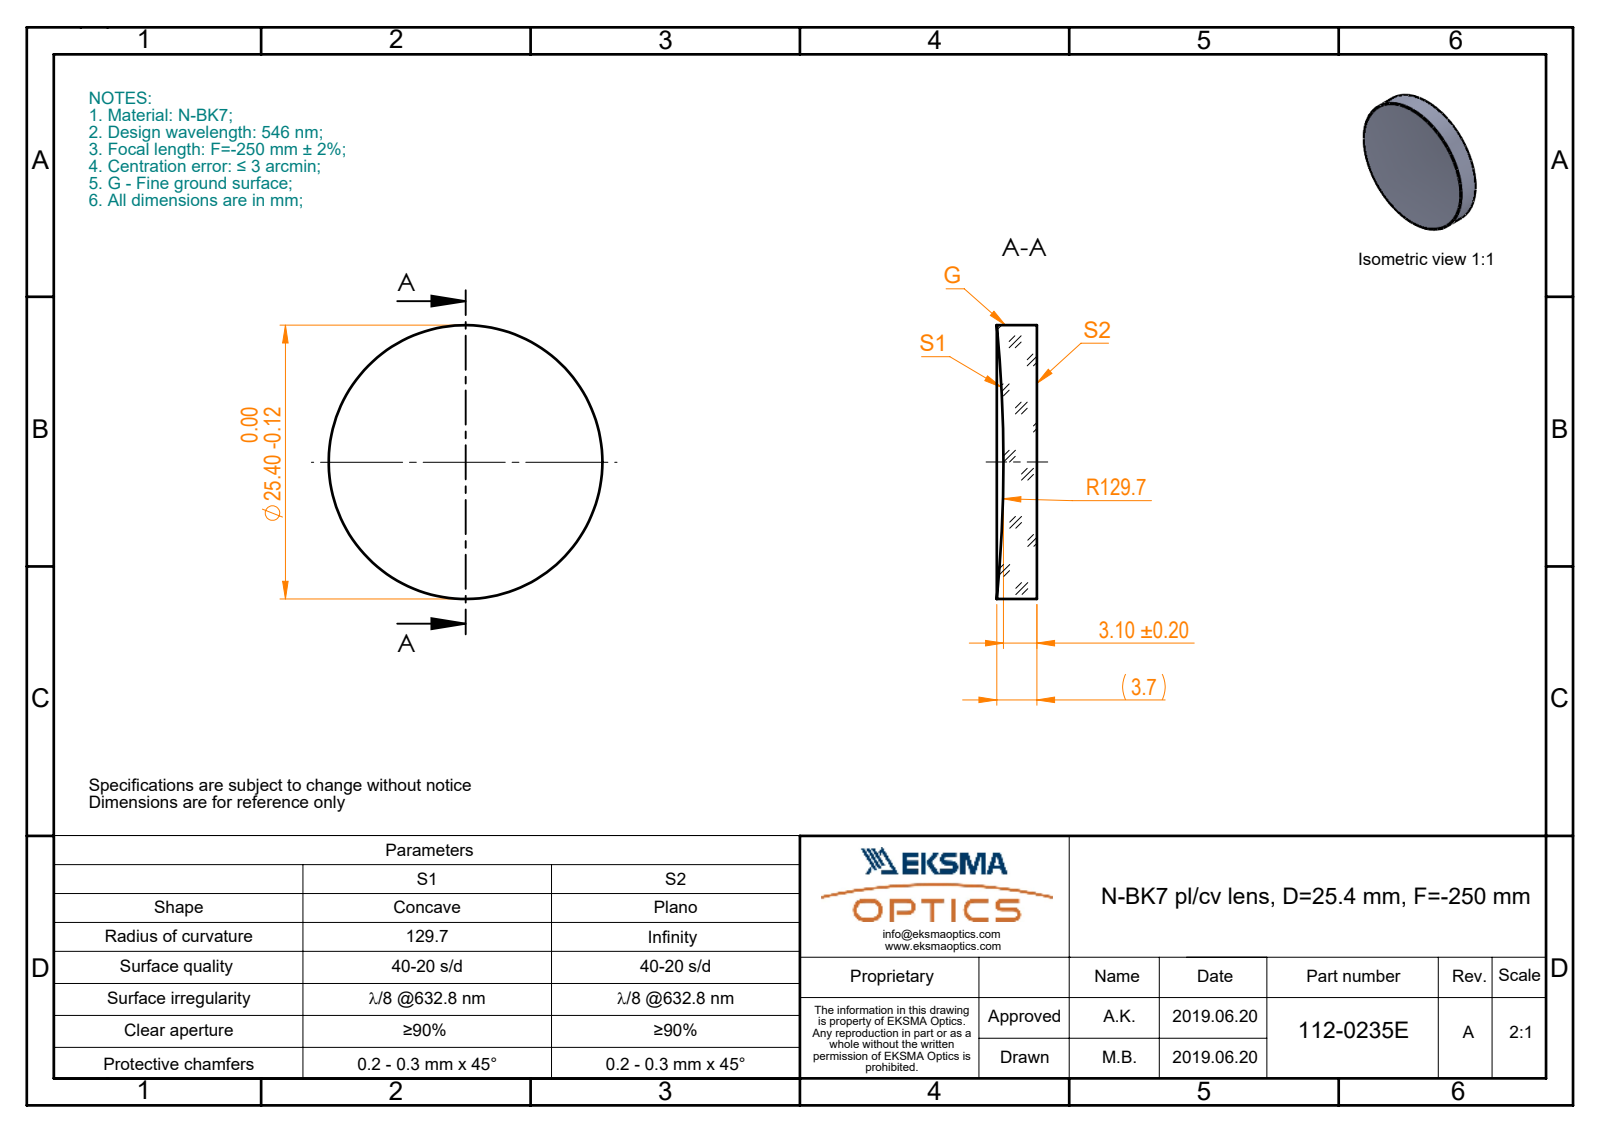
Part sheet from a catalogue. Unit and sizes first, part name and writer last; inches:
Units: inches
Overall size (bounding box): 1 × 1 × 0.146
Round bosses / shafts (diameter × count): ⌀1 ×1
Volume: 0.106 in³ · Surface area: 2.034 in²
Bodies: 1 solid, 5 faces (1 planar, 2 cylindrical, 2 other)
Part name (STEP PRODUCT): 112-0235E BK7 pl-cv 25.4 F-250
STEP written by: SolidWorks 2017 (CONFIG_CONTROL_DESIGN)
